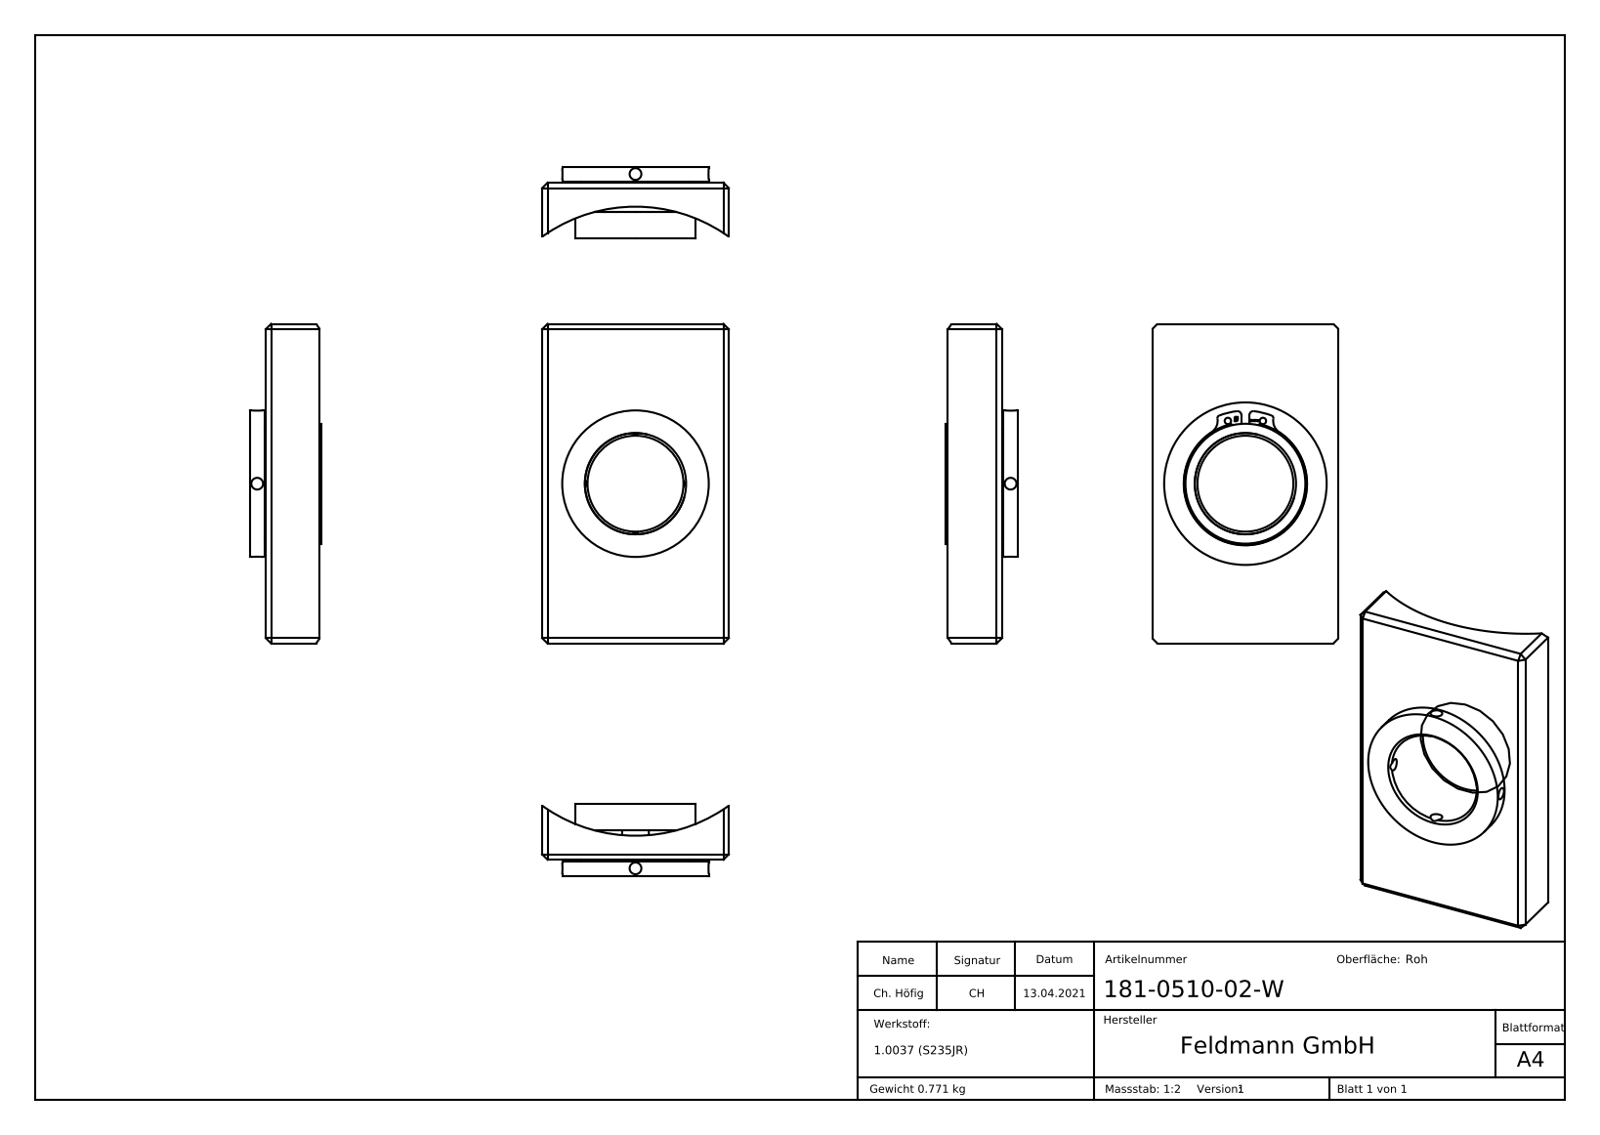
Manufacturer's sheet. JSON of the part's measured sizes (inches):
{"part_name": "181-0510-02-W", "step_written_by": "SolidWorks 2018 (CONFIG_CONTROL_DESIGN)", "units": "inches", "bodies": {"solids": 4, "faces": 363, "planar": 187, "cylindrical": 42, "other": 134}, "overall_size": [4.724, 2.756, 1.063], "volume_in3": 6.029, "surface_area_in2": 55.16, "round_holes": [[0.094, 2], [0.173, 2], [1.417, 1], [1.618, 1], [1.654, 1], [2.402, 1]], "round_bosses_or_shafts": [[2.165, 1], [1.823, 1], [1.772, 1], [1.614, 1]], "partial_cylinders_radius": [[0.039, 2], [0.059, 2], [0.197, 2], [1.079, 1], [2.362, 1]], "face_to_face_distances": [2.756, 0.22, 0.24, 0.02, 0.457, 0.236, 0.217, 4.724, 0.606, 0.827], "hole_center_spacings": [0.963, 0.518]}
